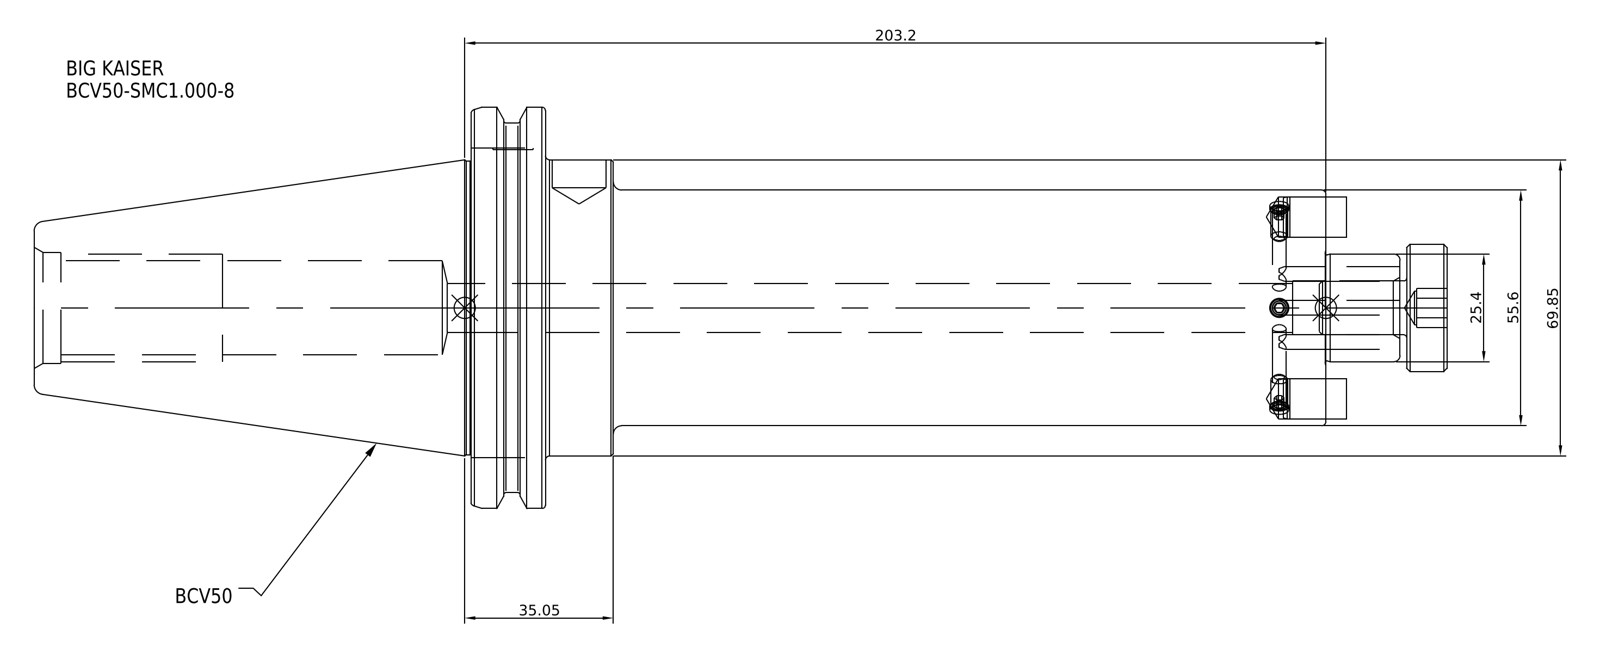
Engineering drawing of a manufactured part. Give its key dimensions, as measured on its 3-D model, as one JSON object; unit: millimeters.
{"part_name": "BCV50-SMC1_000-8", "step_written_by": "SolidWorks 2021 (CONFIG_CONTROL_DESIGN)", "units": "millimeters", "bodies": {"solids": 1, "faces": 38, "planar": 18, "cylindrical": 14, "other": 6}, "overall_size": [309.7, 98.43, 98.43], "volume_mm3": 834334, "surface_area_mm2": 76809, "round_holes": [[11.51, 1]], "round_bosses_or_shafts": [[98.43, 1], [91.29, 1], [69.85, 1], [55.6, 1]], "face_to_face_distances": [17.55, 184.15, 201.7, 168.15, 16, 33.55, 304.8, 136.65, 120.65, 103.1]}
